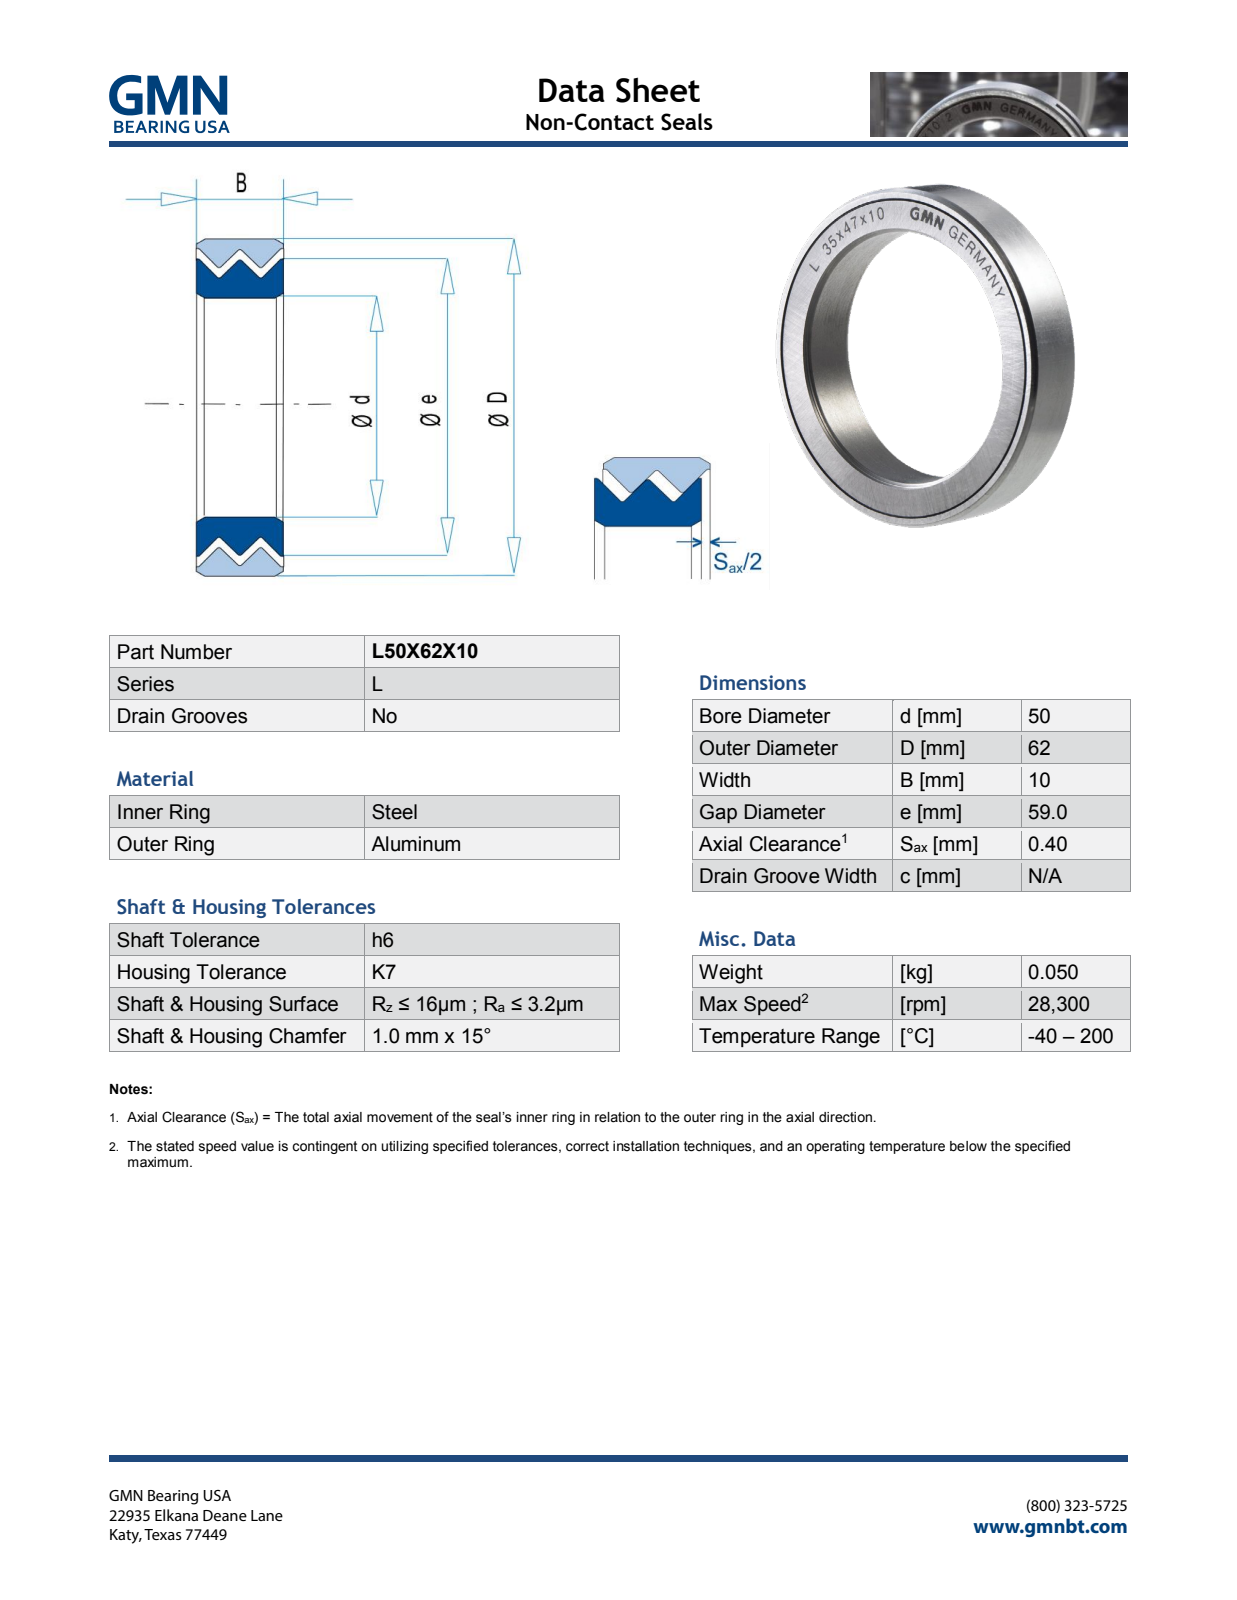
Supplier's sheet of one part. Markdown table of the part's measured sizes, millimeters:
| quantity | value |
| --- | --- |
| part name | L50X62X10_PRT |
| STEP written by | PRO/ENGINEER BY PARAMETRIC TECHNOLOGY CORPORATION, 2013150 (AUTOMOTIVE_DESIGN) |
| units | millimeters |
| bodies | 2 solids, 599 faces (543 planar, 12 cylindrical, 44 other) |
| overall size | 62 × 62 × 10.07 |
| volume | 10 016 mm³ |
| surface area | 10 082 mm² |
| round holes (diameter × count) | 50 × 1, 59.28 × 1 |
| round bosses / shafts (diameter × count) | 62 × 1, 59 × 1 |
| main face-to-face distances | 10, 10.07, 1.68, 1.92, 1.44, 1.93, 1.36, 0.82, 0.86, 1.12 |
